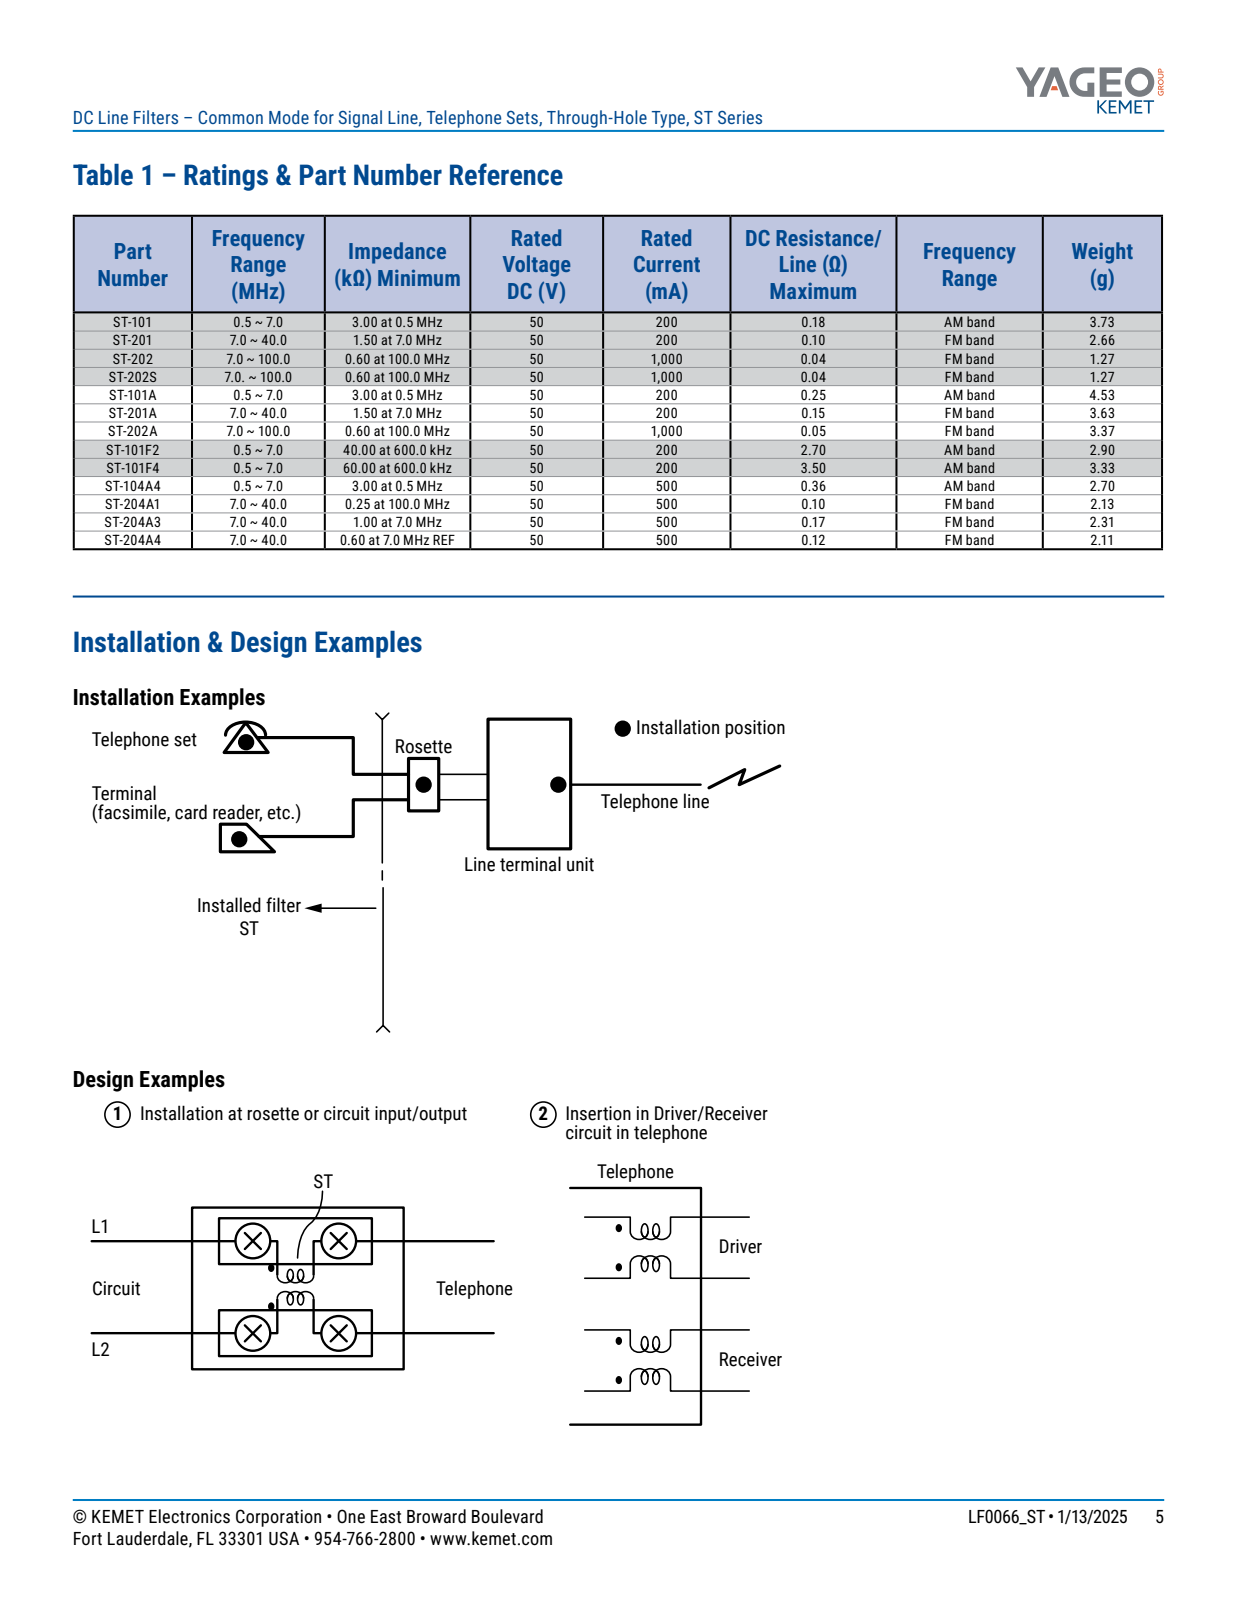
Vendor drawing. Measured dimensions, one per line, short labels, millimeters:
name: IFC_NTST101A_L16W10.5LL4.5
written by: SolidWorks 2014 (AUTOMOTIVE_DESIGN)
unit: mm
bodies: 16 solids, 528 faces (108 planar, 292 cylindrical, 128 other)
size: 24.5 × 16 × 10.5
volume: 1 882 mm³; area: 2 116 mm²
holes: 1× ⌀4.3
bosses: 44× ⌀0.5, 4× ⌀1.2, 4× ⌀0.7, 1× ⌀14.9
rounds: 36× R0.25
face distances: 9.4, 2, 9.56, 0.5, 8.32, 1.01, 1.51, 9.83, 10.33, 8.82
